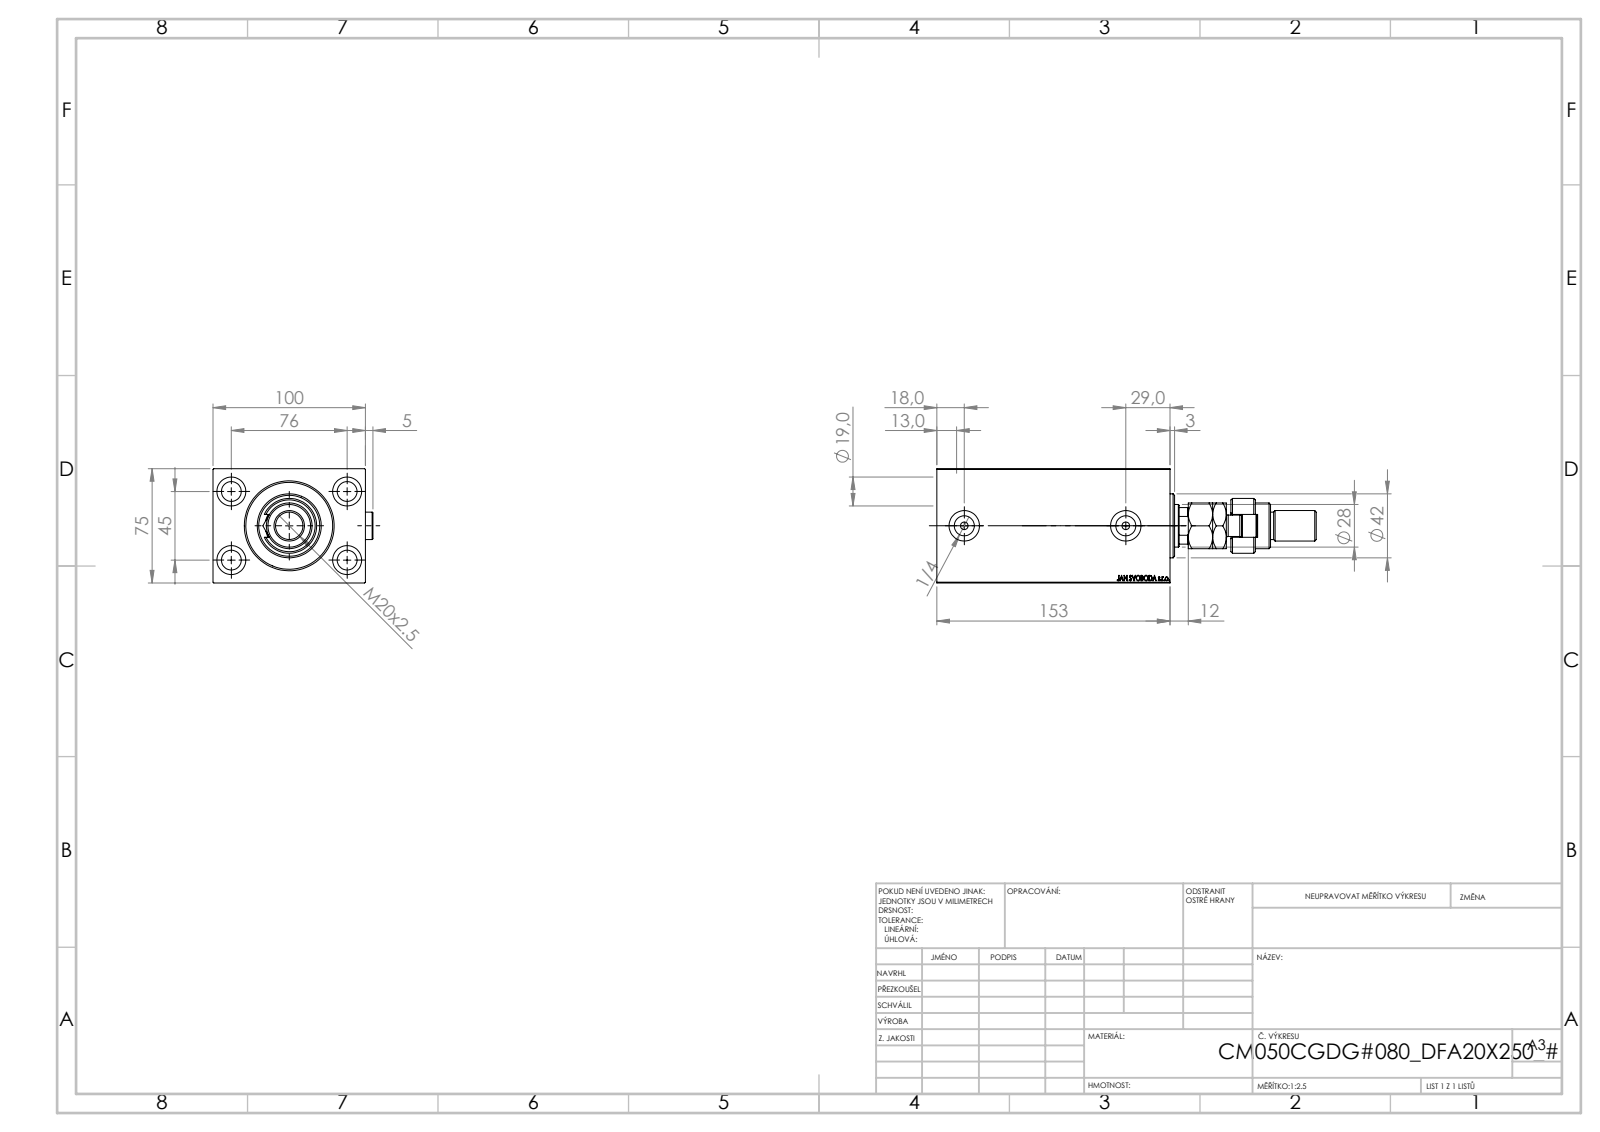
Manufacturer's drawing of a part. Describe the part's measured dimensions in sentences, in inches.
The part is named "Zatka_OIL_PORT; V450CM_C_VCP; V450CM_C_Body; MFA (+2 more)". Its 3-D file was written by "SolidWorks 2019 (CONFIG_CONTROL_DESIGN)". It is 7 solids with 1004 faces: 471 planar, 91 cylindrical and 442 other. Overall it measures 9.803 by 4.13 by 2.953 inches. Its volume is 60.25 cubic inches and its surface area 253.3 square inches. Round holes: 4 of diameter 0.512, 4 of diameter 0.748, 2 of diameter 0.197, 2 of diameter 0.518, 2 of diameter 0.787, 1 of diameter 0.728, 1 of diameter 1.102, 1 of diameter 1.24, 1 of diameter 1.969, 1 of diameter 2.047, 1 of diameter 2.244. Round bosses or shafts: 3 of diameter 0.709, 1 of diameter 1.654, 1 of diameter 1.417, 1 of diameter 1.181, 1 of diameter 0.866, 1 of diameter 0.787, 1 of diameter 0.551. Partial cylindrical surfaces (rounded edges, fillets, slot ends): 1 of radius 0.295, 1 of radius 0.472, 1 of radius 0.531. The main face-to-face distances are 2.953, 3.937, 6.024, 5.472, 0.551, 0.472, 5, 1.181, 5.551, 1.85. The hole center spacings are 1.739, 1.772, 2.992, 3.477, 4.173.
